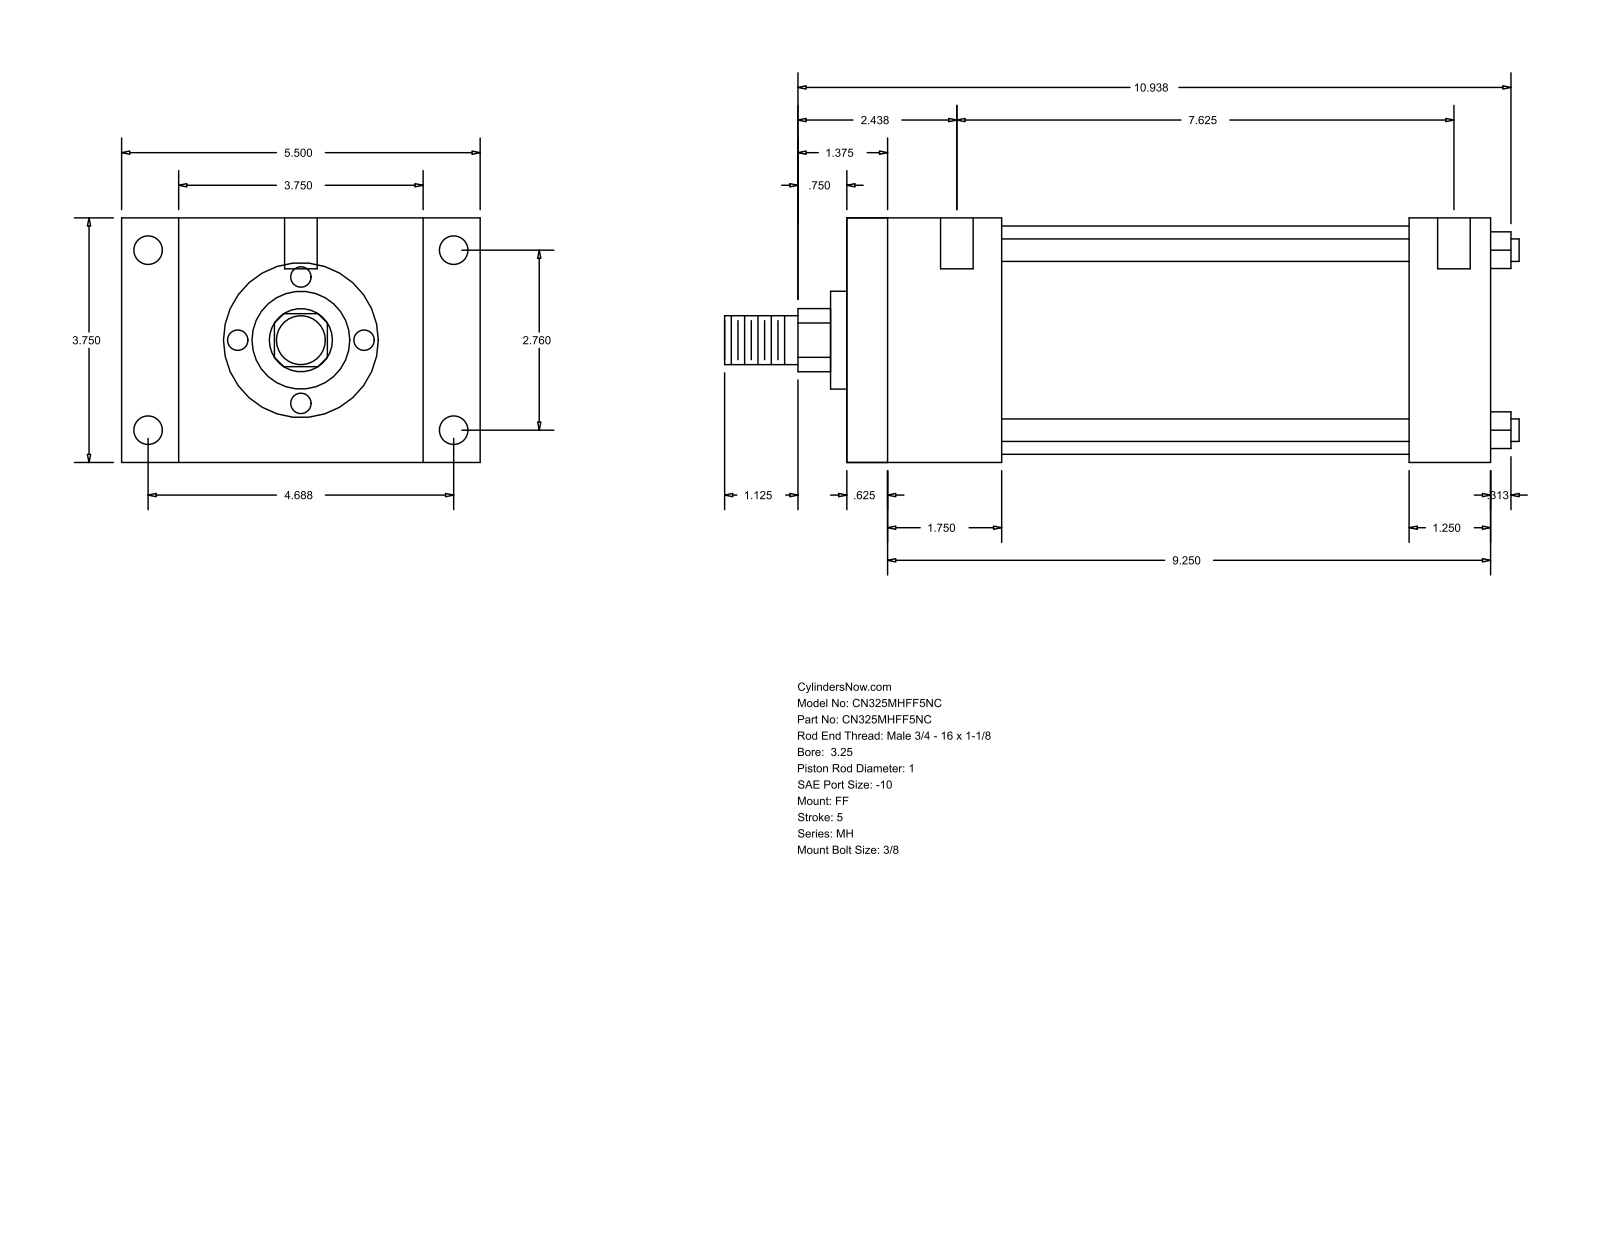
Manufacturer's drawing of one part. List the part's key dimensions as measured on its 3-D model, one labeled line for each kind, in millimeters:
Part name (STEP PRODUCT): MH_FF__0325_1
STEP written by: GSSL Pune (CONFIG_CONTROL_DESIGN)
Units: millimetres
Bodies: 0 solids, 92 faces (64 planar, 28 cylindrical, 0 other)
Overall size (bounding box): 309.56 × 139.7 × 95.25
Round holes (diameter × count): ⌀5.56 ×4, ⌀11.13 ×4, ⌀12.7 ×2
Round bosses / shafts (diameter × count): ⌀8.76 ×4, ⌀88.9 ×1, ⌀38.1 ×1, ⌀25.4 ×1, ⌀19.05 ×1
Partial cylindrical surfaces — rounded edges, fillets, slot ends (radius × count): R12.29 ×1
Main face-to-face distances: 95.24, 250.83, 15.87, 234.96, 22.23, 117.47, 219.07, 203.2, 31.76, 60.33
Hole centre spacings: 70.1, 119.06, 138.16, 200.02, 1.58, 4.76, 193.68, 195.26
